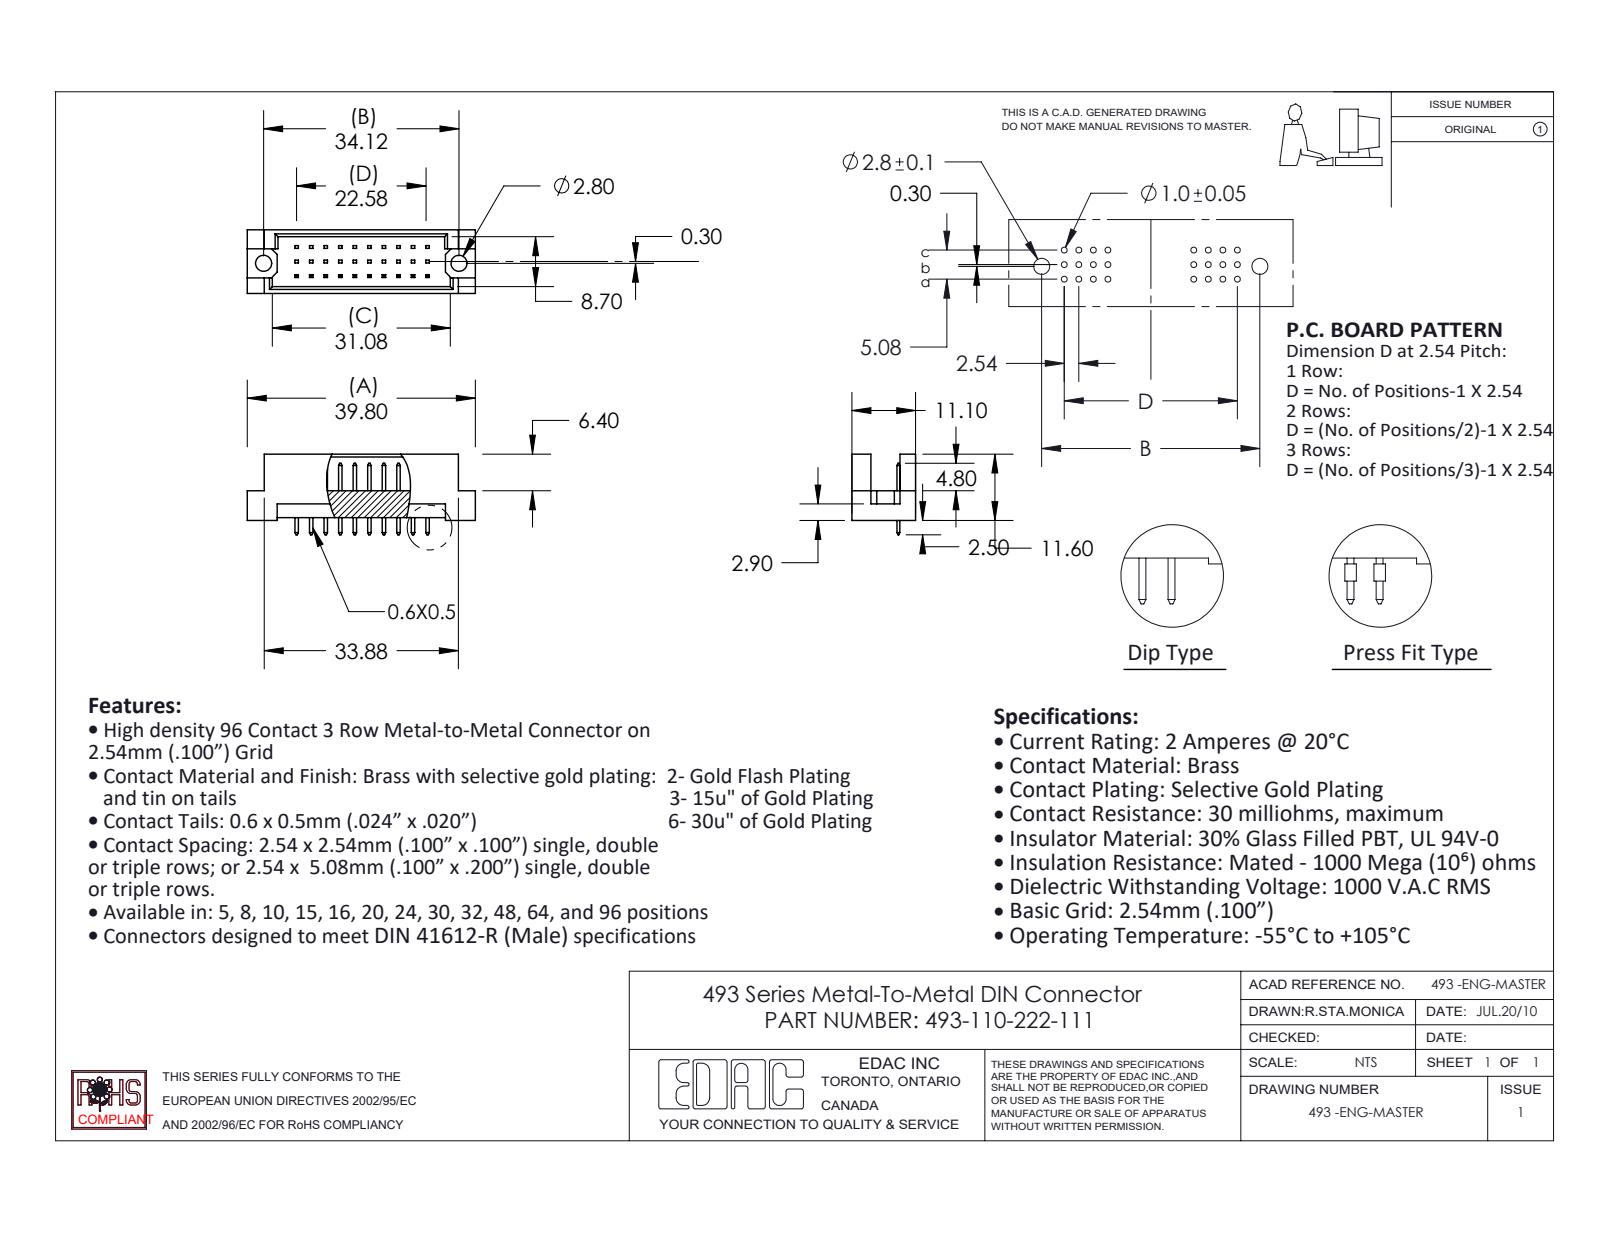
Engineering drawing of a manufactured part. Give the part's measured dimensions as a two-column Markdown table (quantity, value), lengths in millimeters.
| quantity | value |
| --- | --- |
| part name | 493 Part_30; 493-110-222-112; 493-290_22 |
| STEP written by | SolidWorks 2020 (CONFIG_CONTROL_DESIGN) |
| units | millimeters |
| bodies | 11 solids, 312 faces (308 planar, 4 cylindrical, 0 other) |
| overall size | 39.8 × 14.1 × 11.1 |
| volume | 2 409 mm³ |
| surface area | 3 009 mm² |
| round holes (diameter × count) | 2.8 × 2 |
| main face-to-face distances | 1.2, 9.9, 11.1, 8.7, 2.54, 0.5, 4.7, 5.08, 2.76, 3.26 |
| hole center spacings | 34.12 |
